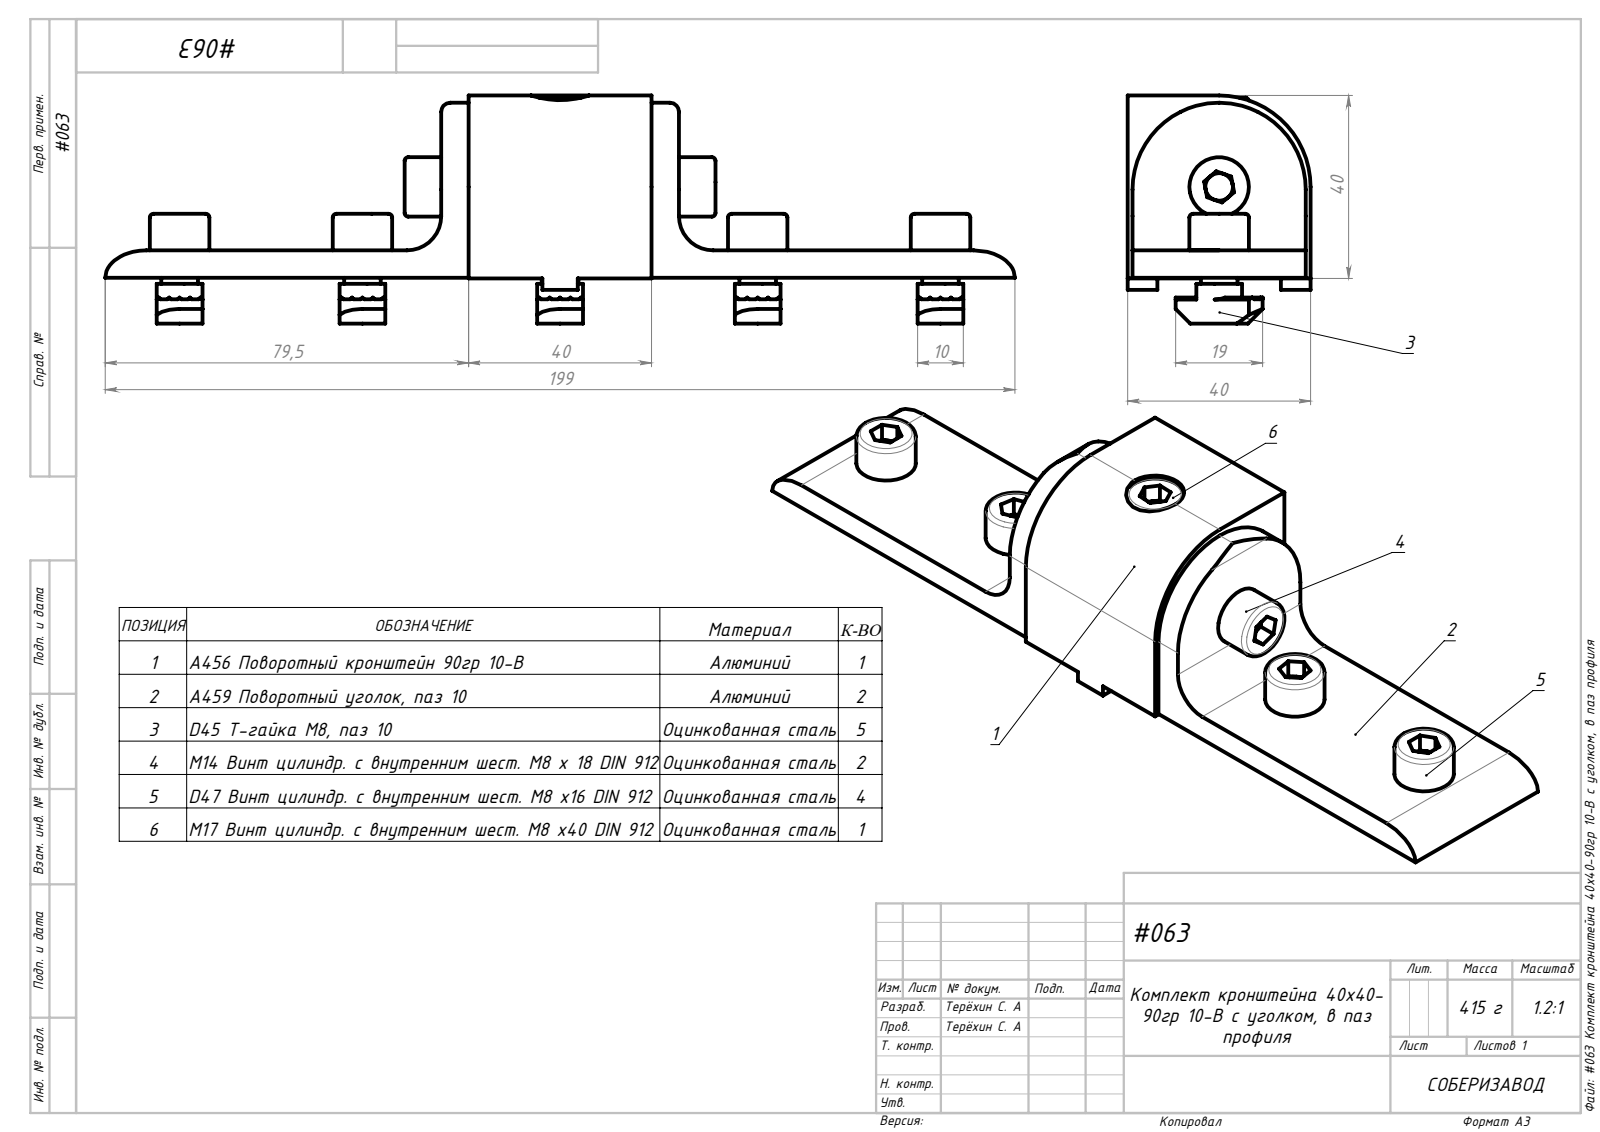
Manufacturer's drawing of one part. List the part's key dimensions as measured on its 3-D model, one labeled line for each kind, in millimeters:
Part name (STEP PRODUCT): #063 Комплект кронштейна 40х40-90гр 10-В с уголком, в паз профиля; D45 Т-гайка М8, паз 10_00; A456 Поворотный кронштейн 90гр 10-B; M14 Винт цилиндр. с внутренним шест. М8 х 18 DIN 912 (+3 more)
STEP written by: SolidWorks 2021 (AUTOMOTIVE_DESIGN)
Units: millimetres
Bodies: 15 solids, 497 faces (322 planar, 87 cylindrical, 88 other)
Overall size (bounding box): 199 × 49.88 × 40
Volume: 121 448 mm³ · Surface area: 42 623 mm²
Round holes (diameter × count): ⌀6.7 ×5, ⌀8.35 ×5, ⌀7.2 ×1, ⌀8.25 ×1, ⌀12.7 ×1
Round bosses / shafts (diameter × count): ⌀13 ×6, ⌀8 ×6
Partial cylindrical surfaces — rounded edges, fillets, slot ends (radius × count): R5.67 ×10, R6 ×10, R2 ×2, R7.5 ×2, R19 ×2, R20 ×1
Main face-to-face distances: 6, 40, 1.05, 38.95, 46, 6.13, 37.9, 10, 52, 39.87
Hole centre spacings: 40, 126.45, 39.99, 40.01, 43.22, 43.23, 83.22, 83.23
